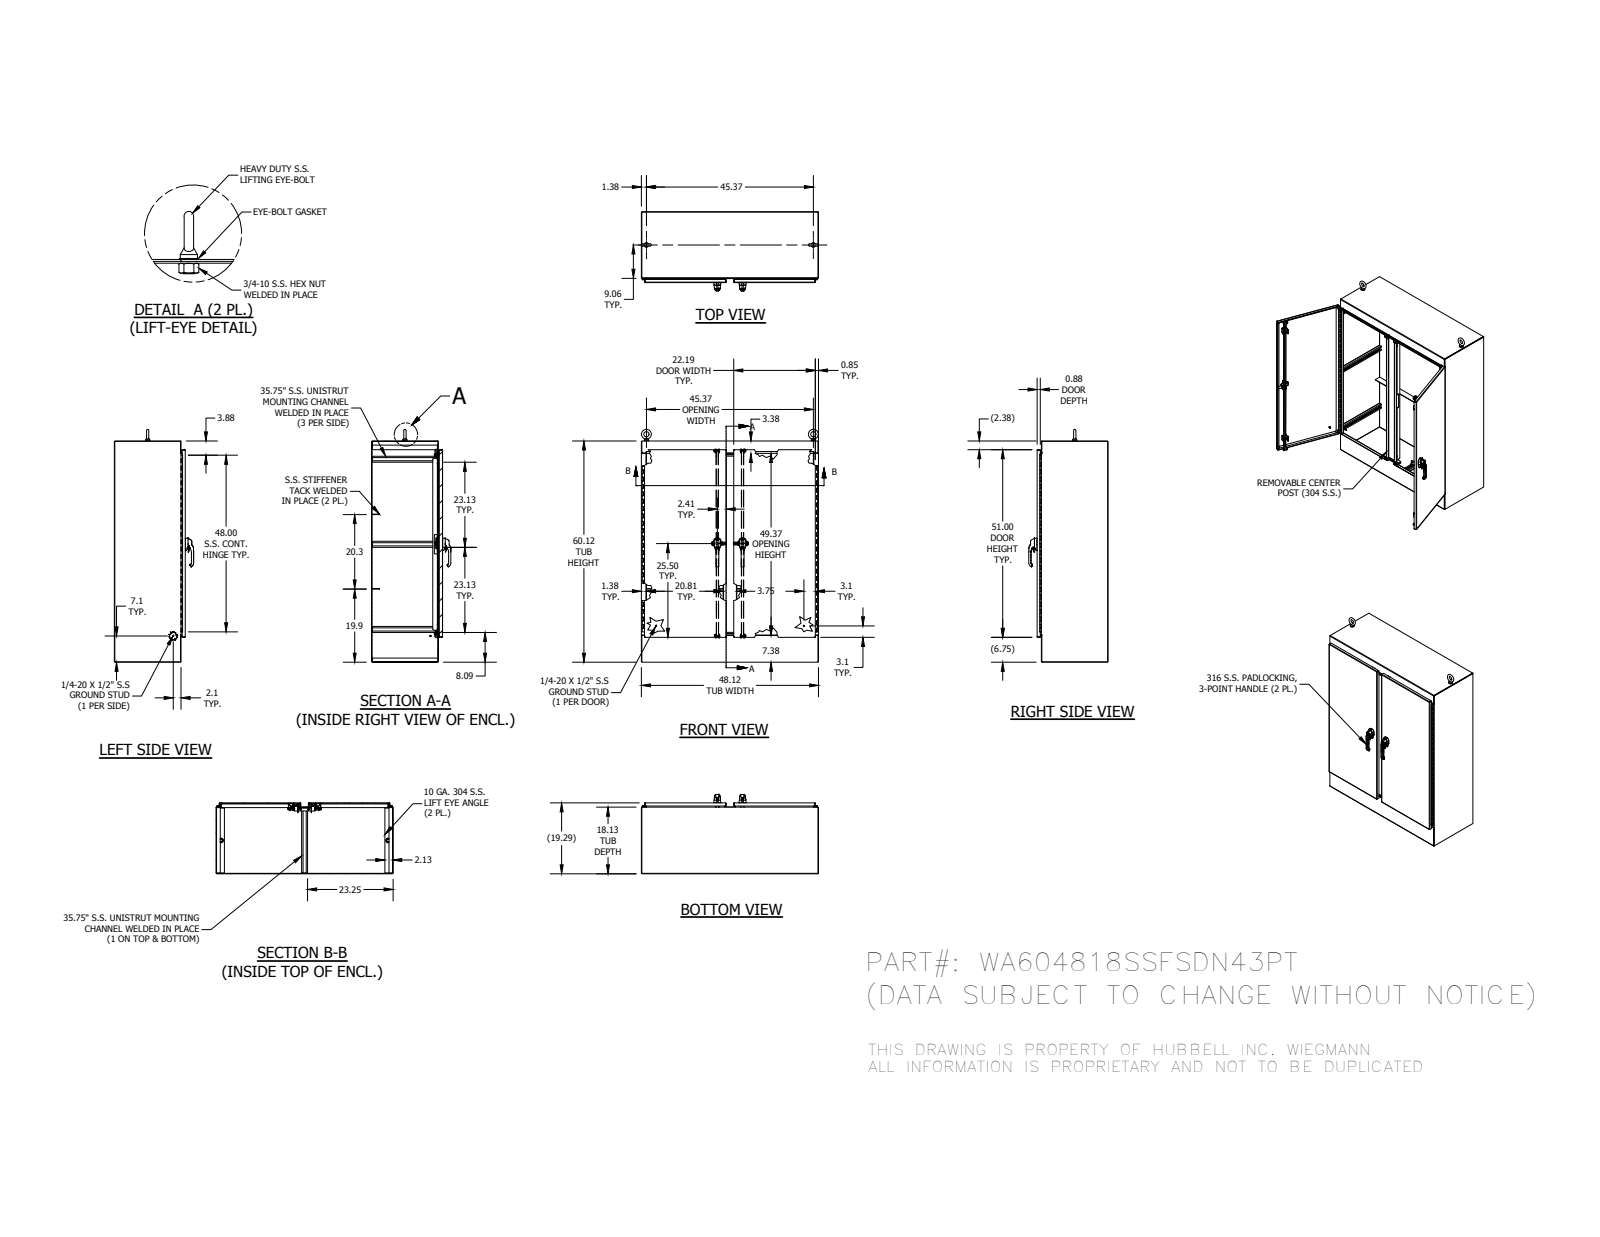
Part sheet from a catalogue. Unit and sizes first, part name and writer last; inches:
Units: inches
Overall size (bounding box): 63.248 × 48.125 × 21.541
Round holes (diameter × count): ⌀0.262 ×16, ⌀0.375 ×16, ⌀0.187 ×8, ⌀0.213 ×6, ⌀0.281 ×6, ⌀0.25 ×5, ⌀0.196 ×4, ⌀0.241 ×4, ⌀0.252 ×4, ⌀0.281 ×4, ⌀0.315 ×4, ⌀0.4 ×4
Round bosses / shafts (diameter × count): ⌀0.25 ×7, ⌀0.533 ×6, ⌀0.236 ×6, ⌀1 ×5, ⌀0.563 ×4, ⌀0.531 ×4, ⌀0.5 ×4, ⌀0.438 ×4
Partial cylindrical surfaces — rounded edges, fillets, slot ends (radius × count): R0.02 ×350, R0.012 ×213, R0.019 ×44, R0.125 ×44, R0.05 ×34, R0.079 ×28, R0.025 ×24, R0.059 ×23
Main face-to-face distances: 0.125, 0.125, 19.167, 48, 18, 1.167, 60, 47.875, 19.165, 19.04
Hole centre spacings: 42.49, 43.24, 16, 0.38, 0.38, 5.333, 0.76, 10.667
Volume: 1 528 in³ · Surface area: 24 990 in²
Bodies: 133 solids, 6856 faces (2530 planar, 2630 cylindrical, 1696 other)
Part name (STEP PRODUCT): HFW372182; WA6048SSFSDN43PTLDR; 38846; 1091-903_AF0_1 (+8 more)
STEP written by: SolidWorks 2014 (AUTOMOTIVE_DESIGN)
